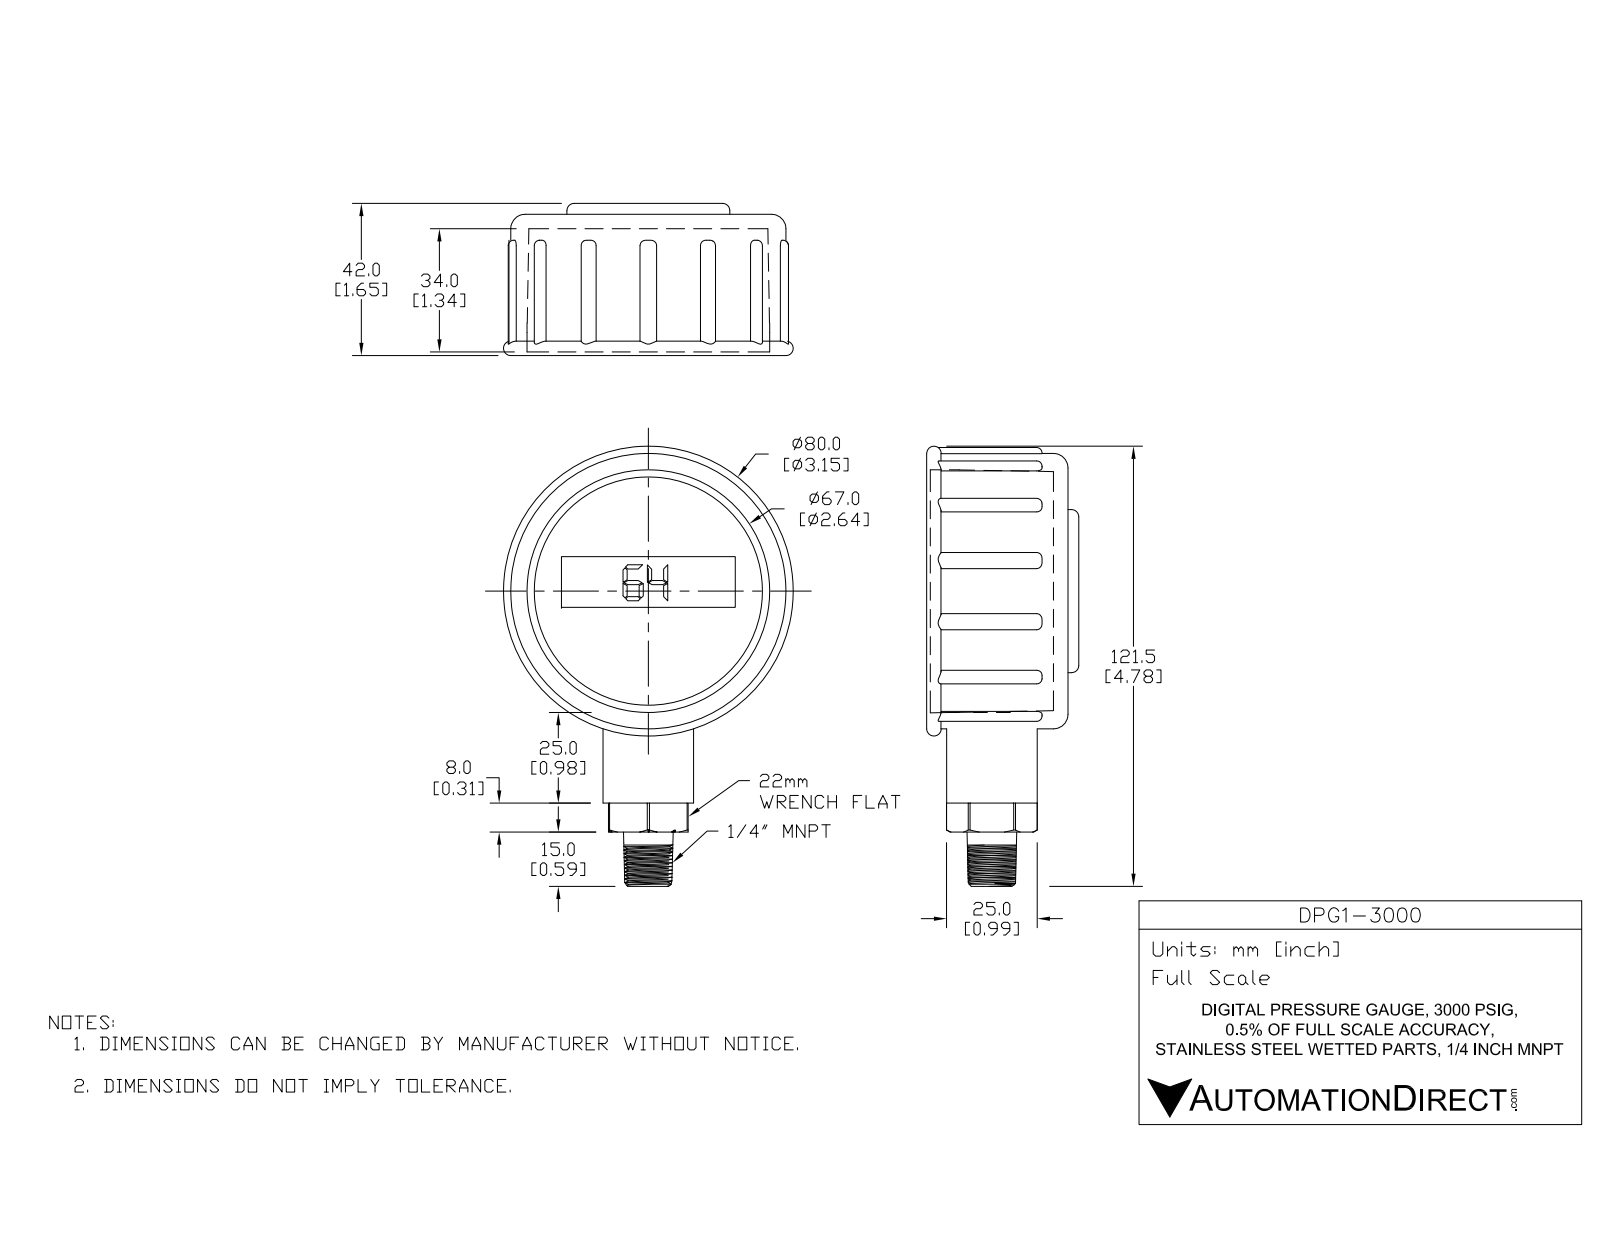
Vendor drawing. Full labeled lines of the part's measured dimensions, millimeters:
Part name (STEP PRODUCT): DPG1-3000
STEP written by: SolidWorks 2021 (CONFIG_CONTROL_DESIGN)
Units: millimetres
Bodies: 4 solids, 181 faces (71 planar, 49 cylindrical, 61 other)
Overall size (bounding box): 121.62 × 80 × 42
Volume: 196 180 mm³ · Surface area: 45 978 mm²
Round holes (diameter × count): ⌀63 ×1, ⌀67.19 ×1
Round bosses / shafts (diameter × count): ⌀76 ×1, ⌀67 ×1, ⌀45 ×1, ⌀25 ×1, ⌀10 ×1
Partial cylindrical surfaces — rounded edges, fillets, slot ends (radius × count): R2.38 ×13, R8.5 ×6, R38 ×1
Main face-to-face distances: 33.95, 4, 37.95, 3, 7, 40.95, 42, 39, 35, 1.05
